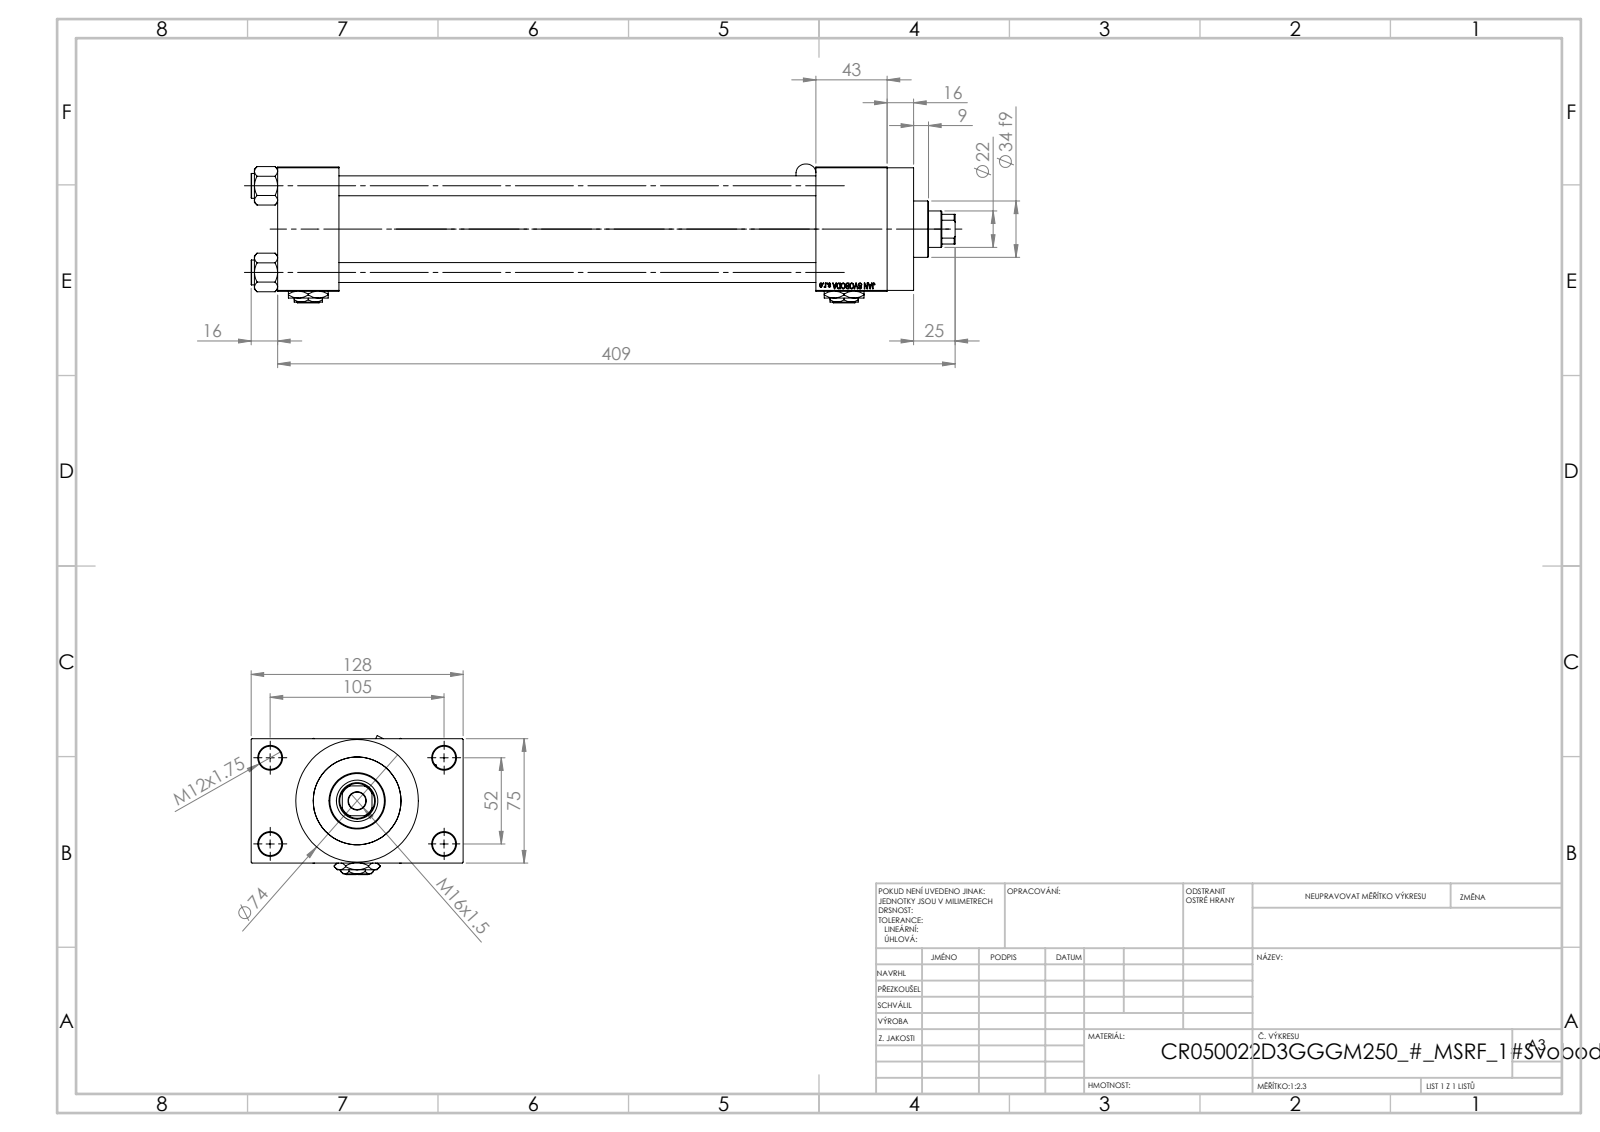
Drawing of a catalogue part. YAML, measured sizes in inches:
part_name: "NUT_M5_D; V215CR_D_TYCINKA; Zatka_pro_OIL_PORT; V215_VC_A (+3 more)"
step_written_by: "SolidWorks 2019 (CONFIG_CONTROL_DESIGN)"
units: inches
bodies: {solids: 14, faces: 1237, planar: 563, cylindrical: 114, other: 560}
overall_size: [16.732, 5.039, 3.302]
volume: 67.86
surface_area: 462.8
round_holes:
  - {diameter: 0.472, count: 4}
  - {diameter: 0.551, count: 4}
  - {diameter: 0.276, count: 2}
  - {diameter: 0.825, count: 2}
  - {diameter: 1.181, count: 2}
  - {diameter: 0.413, count: 1}
  - {diameter: 0.866, count: 1}
  - {diameter: 0.984, count: 1}
  - {diameter: 1.614, count: 1}
  - {diameter: 1.969, count: 1}
  - {diameter: 2.087, count: 1}
round_bosses_or_shafts:
  - {diameter: 0.591, count: 4}
  - {diameter: 2.913, count: 1}
  - {diameter: 2.205, count: 1}
  - {diameter: 1.339, count: 1}
  - {diameter: 0.197, count: 1}
  - {diameter: 0.098, count: 1}
partial_cylinders:
  - {radius: 0.02, count: 6}
  - {radius: 0.236, count: 2}
  - {radius: 0.413, count: 1}
face_to_face_distances: [2.953, 11.339, 1.457, 12.795, 1.043, 3.996, 14.488, 13.031, 1.693, 0.63]
hole_center_spacings: [1.037, 1.456, 2.059, 2.3, 2.307, 3.096, 3.715, 2.047]
